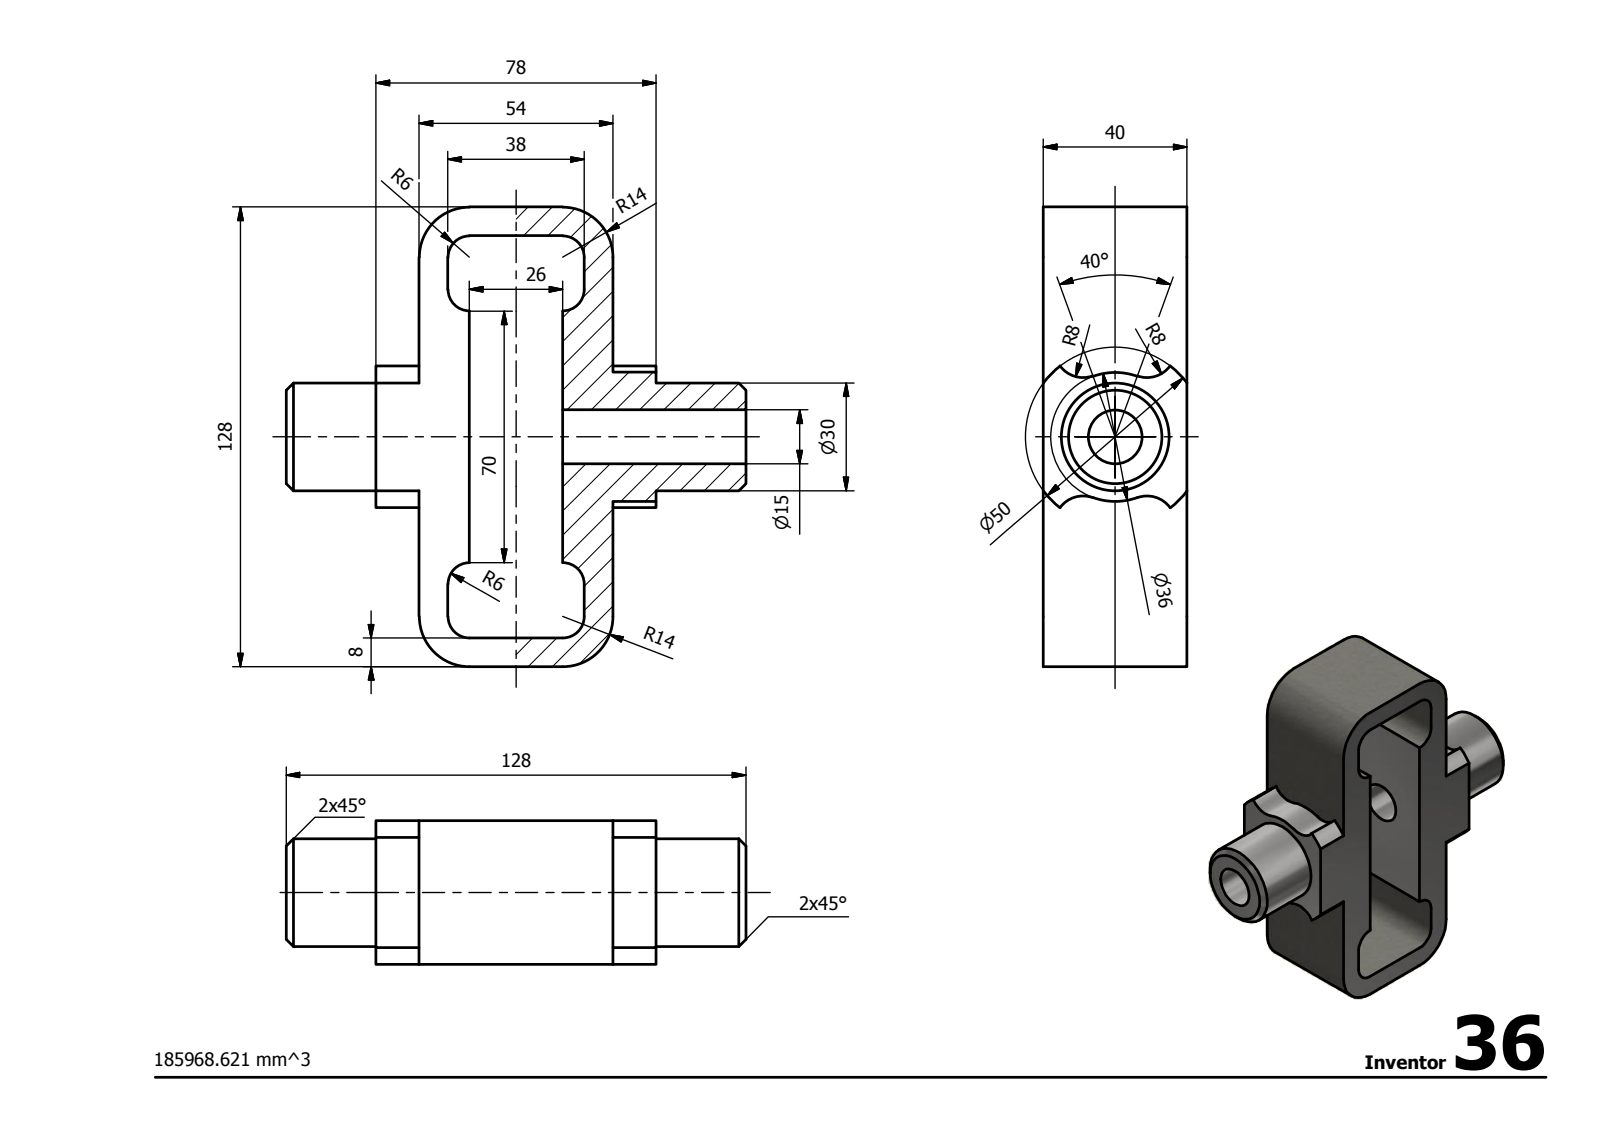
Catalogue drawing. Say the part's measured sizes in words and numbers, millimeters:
Its 3-D file was written by "Autodesk Inventor 2014 (AUTOMOTIVE_DESIGN)". It is 1 solid with 58 faces: 20 planar, 36 cylindrical and 2 other. Overall it measures 128 by 128 by 40 millimeters. Its volume is 185 968 cubic millimeters and its surface area 44 767 square millimeters. Round holes: 1 of diameter 15. Round bosses or shafts: 1 of diameter 30. Partial cylindrical surfaces (rounded edges, fillets, slot ends): 8 of radius 6, 4 of radius 8, 4 of radius 14, 1 of radius 18, 1 of radius 25. The main face-to-face distances are 40, 14, 26, 8, 54, 120, 46, 6, 32, 128.
